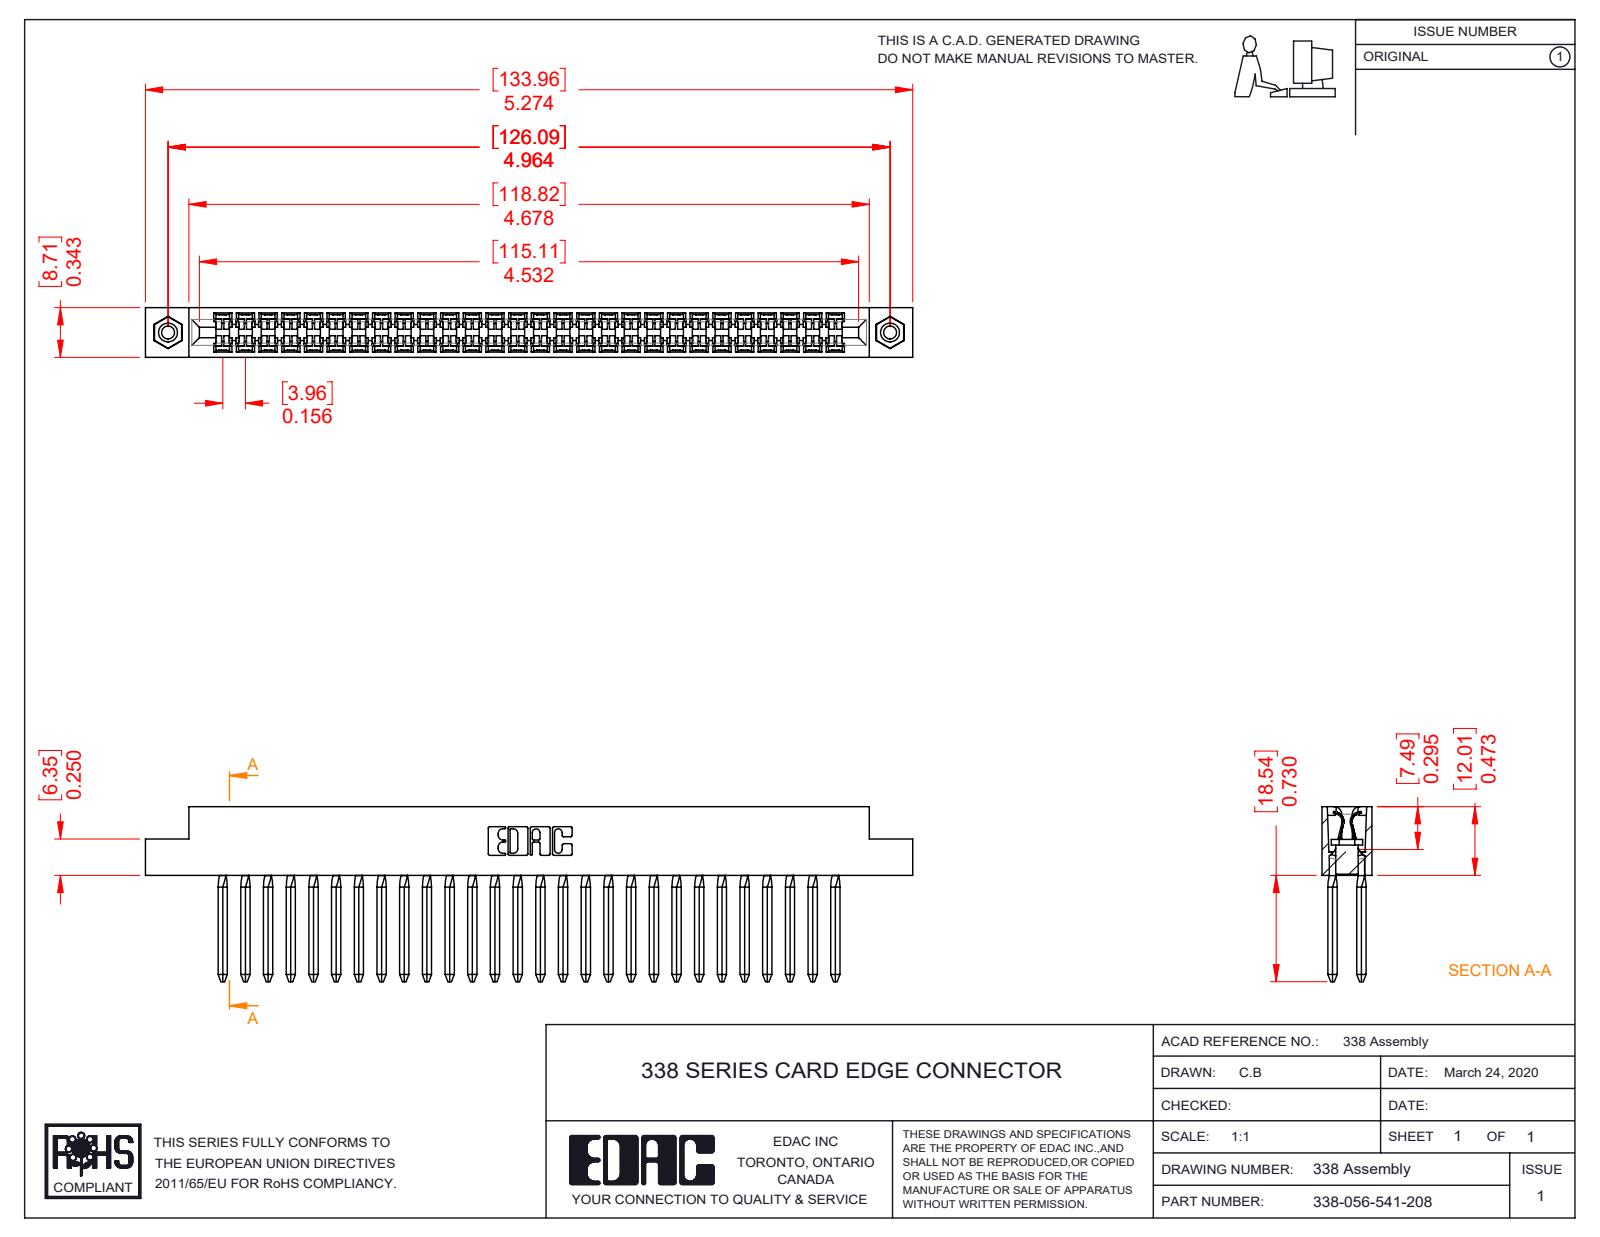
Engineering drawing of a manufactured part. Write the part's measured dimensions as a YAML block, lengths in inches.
part_name: "338-210-001_338-210-028-004; 338-290-001_541; 338-056-541-208; 345-250-001_345-250-003-102"
step_written_by: "SolidWorks 2016 (CONFIG_CONTROL_DESIGN)"
units: inches
bodies: {solids: 59, faces: 3906, planar: 2714, cylindrical: 952, other: 240}
overall_size: [5.274, 1.203, 0.343]
volume: 0.632
surface_area: 30.26
round_holes:
  - {diameter: 0.089, count: 2}
  - {diameter: 0.125, count: 2}
  - {diameter: 0.156, count: 2}
round_bosses_or_shafts:
  - {diameter: 0.155, count: 2}
partial_cylinders:
  - {radius: 0.025, count: 170}
  - {radius: 0.008, count: 56}
  - {radius: 0.055, count: 46}
  - {radius: 0.067, count: 46}
  - {radius: 0.1, count: 44}
  - {radius: 0.01, count: 22}
  - {radius: 0.007, count: 6}
  - {radius: 0.031, count: 6}
face_to_face_distances: [0.343, 0.156, 0.11, 0.207, 0.135, 0.624, 0.78, 0.16, 0.468, 0.048]
hole_center_spacings: [4.964]
